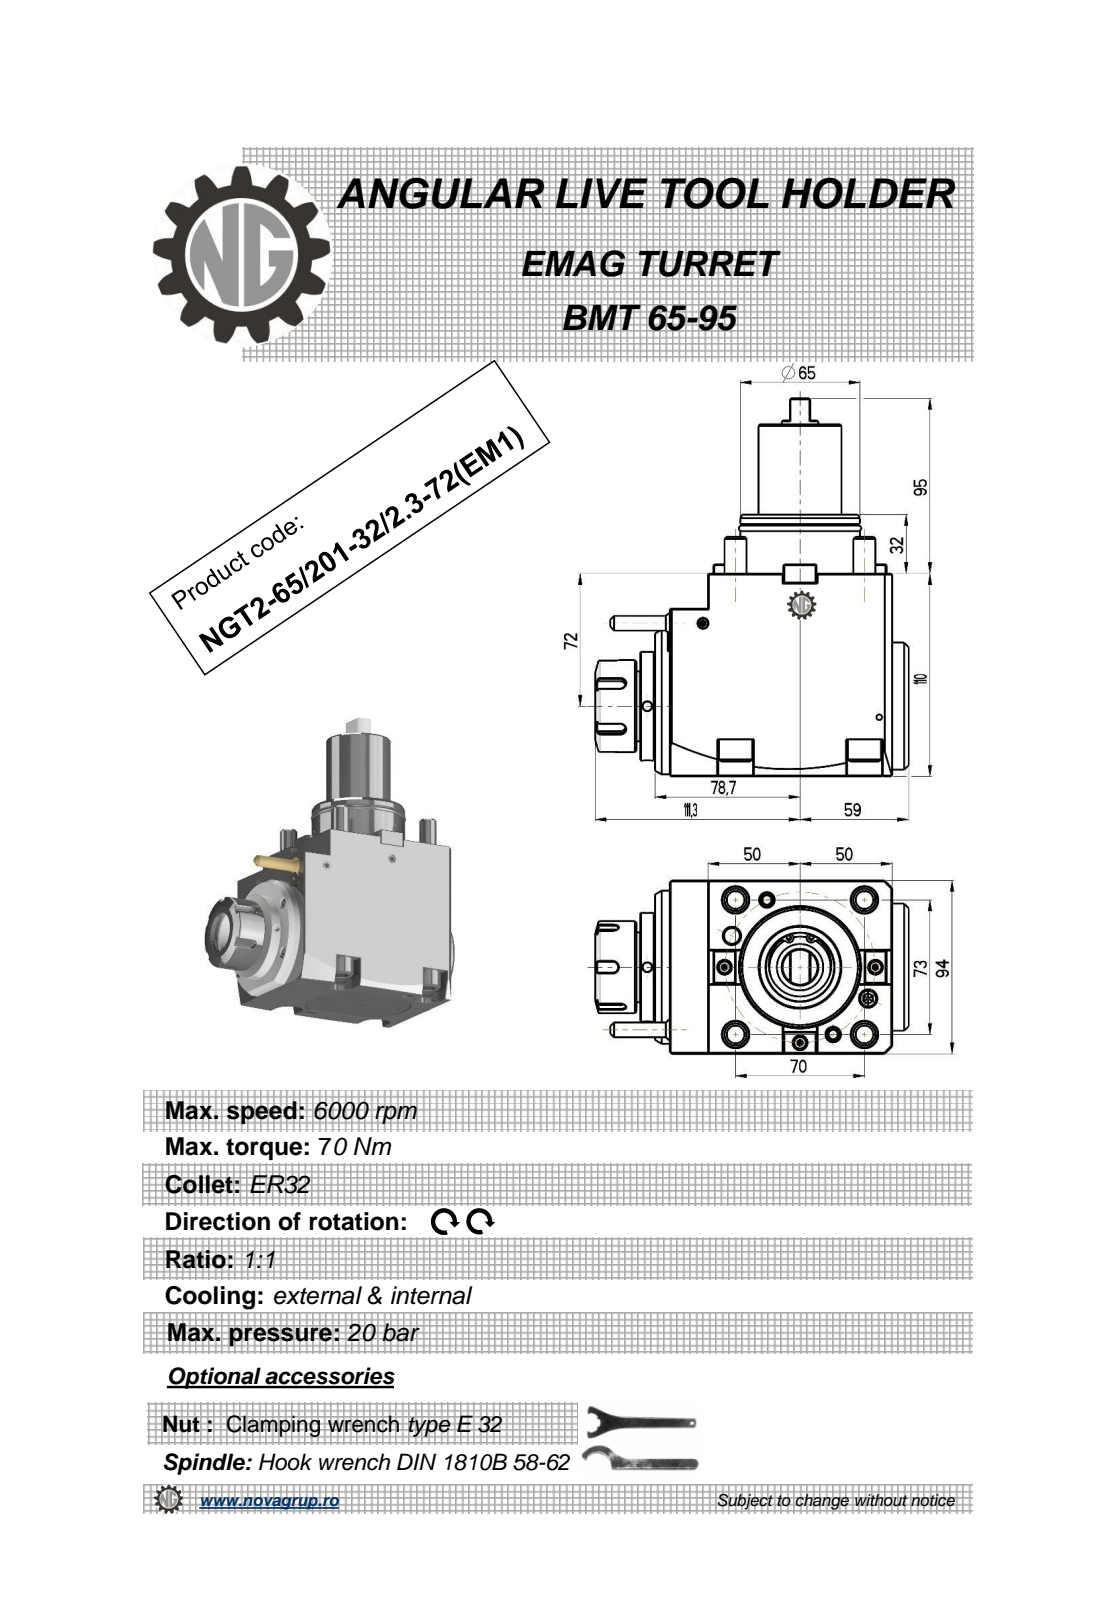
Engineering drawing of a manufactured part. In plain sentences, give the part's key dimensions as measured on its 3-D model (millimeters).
The part is named "NGT2_65_201_32_1_3_72_EM1". Its 3-D file was written by "PRO/ENGINEER BY PARAMETRIC TECHNOLOGY CORPORATION, 2010280 (CONFIG_CONTROL_DESIGN)". It is 2 solids with 442 faces: 216 planar, 110 cylindrical and 116 other. Overall it measures 205 by 170.3 by 94 millimeters. Its volume is 1 525 000 cubic millimeters and its surface area 109 699 square millimeters. Round holes: 3 of diameter 5, 2 of diameter 8.5, 1 of diameter 3, 1 of diameter 27. Round bosses or shafts: 4 of diameter 18, 4 of diameter 12, 1 of diameter 83, 1 of diameter 69, 1 of diameter 65, 1 of diameter 60, 1 of diameter 59, 1 of diameter 50. Partial cylindrical surfaces (rounded edges, fillets, slot ends): 20 of radius 0.36, 6 of radius 0.22, 5 of radius 3, 4 of radius 9.5, 2 of radius 0.8, 2 of radius 550. The main face-to-face distances are 94, 110, 8, 9, 128.7, 137.7, 100, 120.7, 129.7, 19. The hole center spacings are 48.99, 56.4, 81.44, 121.15.
